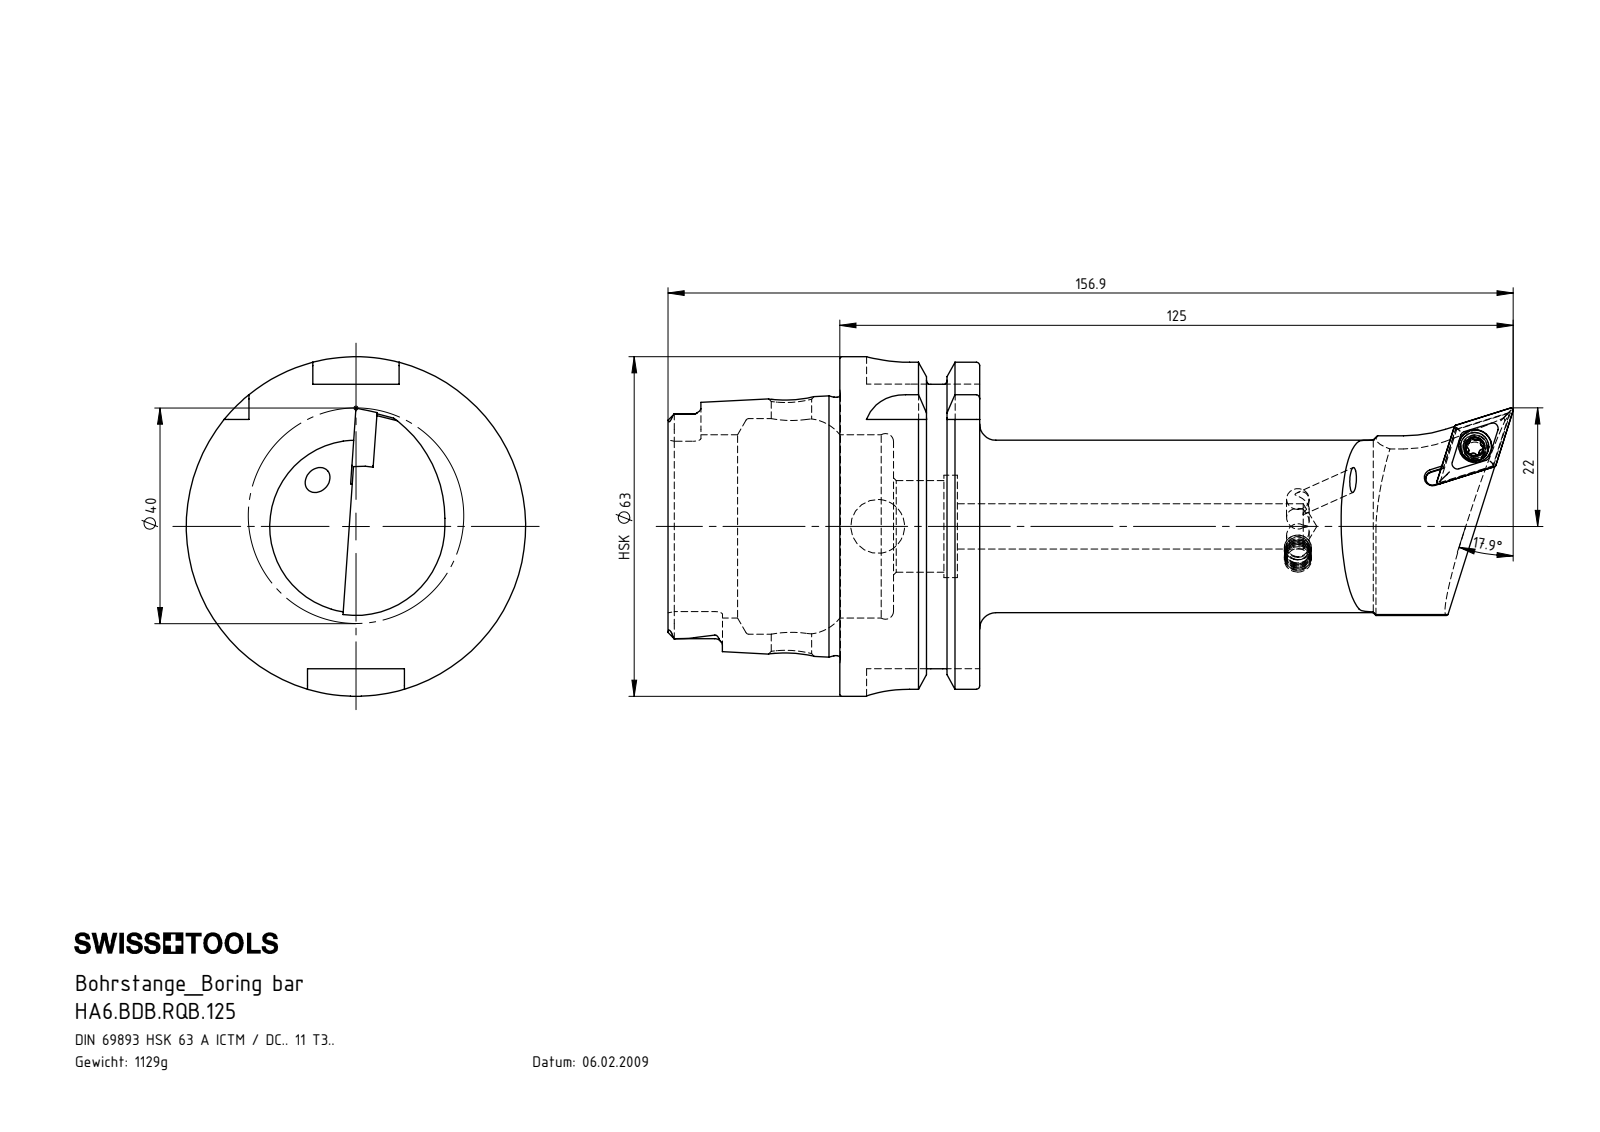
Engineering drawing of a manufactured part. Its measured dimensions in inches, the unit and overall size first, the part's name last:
Units: inches
Overall size (bounding box): 6.177 × 2.48 × 2.48
Round holes (diameter × count): ⌀0.165 ×2, ⌀0.13 ×1, ⌀0.157 ×1, ⌀0.173 ×1, ⌀0.197 ×1, ⌀0.24 ×1, ⌀0.295 ×1, ⌀0.331 ×1, ⌀0.394 ×1, ⌀0.669 ×1, ⌀0.748 ×1, ⌀1.339 ×1
Round bosses / shafts (diameter × count): ⌀2.48 ×1, ⌀2.163 ×1, ⌀1.887 ×1, ⌀1.26 ×1, ⌀0.207 ×1, ⌀0.197 ×1, ⌀0.157 ×1
Partial cylindrical surfaces — rounded edges, fillets, slot ends (radius × count): R0.013 ×6, R0.023 ×6, R0.055 ×6, R0.315 ×4, R0.111 ×2, R0.113 ×2, R0.049 ×1, R0.118 ×1
Main face-to-face distances: 1.022, 0.63, 0.392, 1.256, 1.648, 2.278, 2.079, 0.858, 0.467, 2.114
Volume: 8.762 in³ · Surface area: 53.11 in²
Bodies: 5 solids, 308 faces (79 planar, 90 cylindrical, 139 other)
Part name (STEP PRODUCT): HA6-BDB.RQB.125_B; WCB-ER2.001.009_A; DCMT11T304; KVT_MB_600_050 (+1 more)
STEP written by: SolidWorks 2017 (AUTOMOTIVE_DESIGN)
